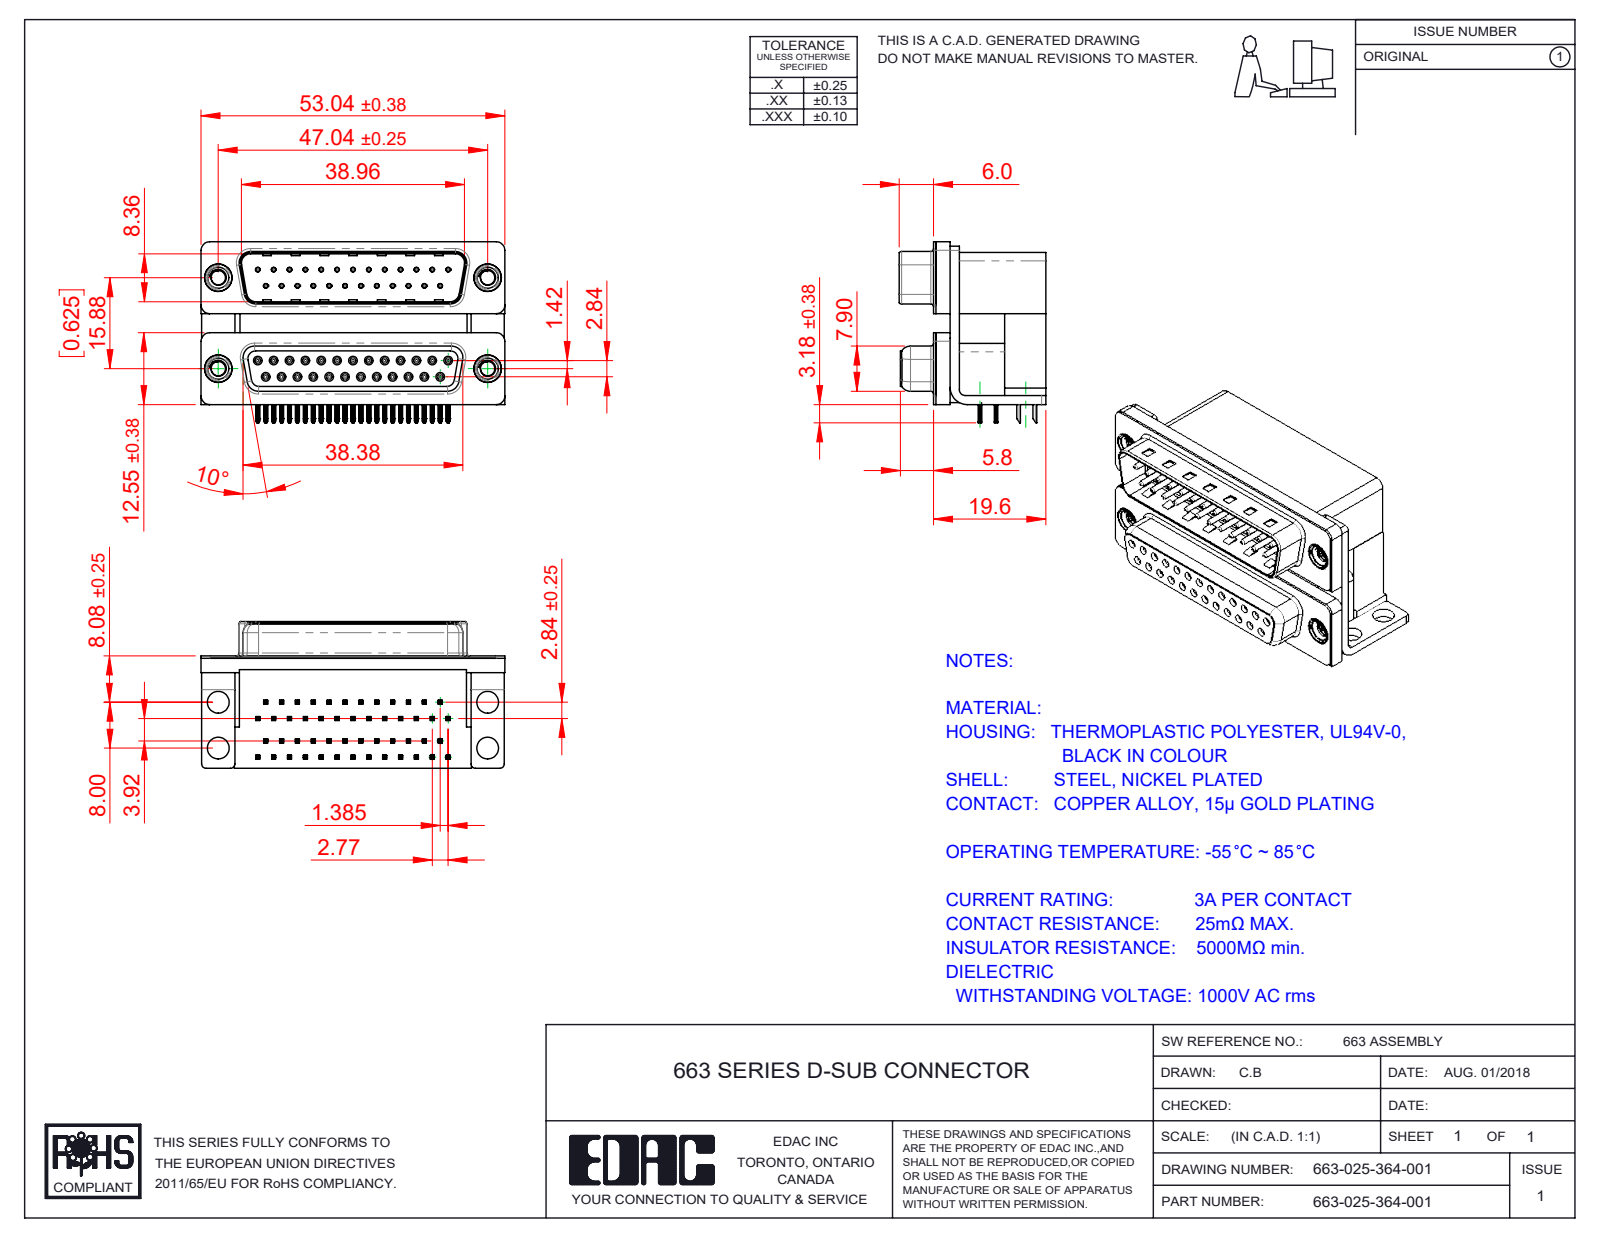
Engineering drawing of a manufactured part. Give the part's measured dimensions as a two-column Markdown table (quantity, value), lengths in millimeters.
| quantity | value |
| --- | --- |
| part name | 663 Housing Upper_25 Contacts L; 663 Contact Bottom Upper_L; 663 Shell Receptacle_25 Contacts; 663 Housing Spacer_25 Contacts L (+8 more) |
| STEP written by | SolidWorks 2020 (CONFIG_CONTROL_DESIGN) |
| units | millimeters |
| bodies | 61 solids, 6207 faces (3257 planar, 1551 cylindrical, 1399 other) |
| overall size | 53.04 × 31.61 × 25.6 |
| volume | 21 595 mm³ |
| surface area | 22 989 mm² |
| round holes (diameter × count) | 0.8 × 50, 0.35 × 25, 0.9 × 25, 2.5 × 4, 3.5 × 4, 3.8 × 4, 4 × 4, 4.8 × 4, 5 × 4 |
| round bosses / shafts (diameter × count) | 1.2 × 25, 0.75 × 25, 4.9 × 4, 4.75 × 4, 3.9 × 4 |
| partial cylindrical surfaces (radius × count) | 0.1 × 200, 0.15 × 100, 0.25 × 100, 0.12 × 50, 0.35 × 50, 0.34 × 25, 1.5 × 13, 0.28 × 12 |
| main face-to-face distances | 0.4, 19.2, 7.2, 12, 10.7, 16.7, 9.5, 2.5, 15.53, 26.23 |
| hole center spacings | 3.16, 2.77, 5.54, 11.08, 8.31, 5.03, 13.85, 7.48 |
